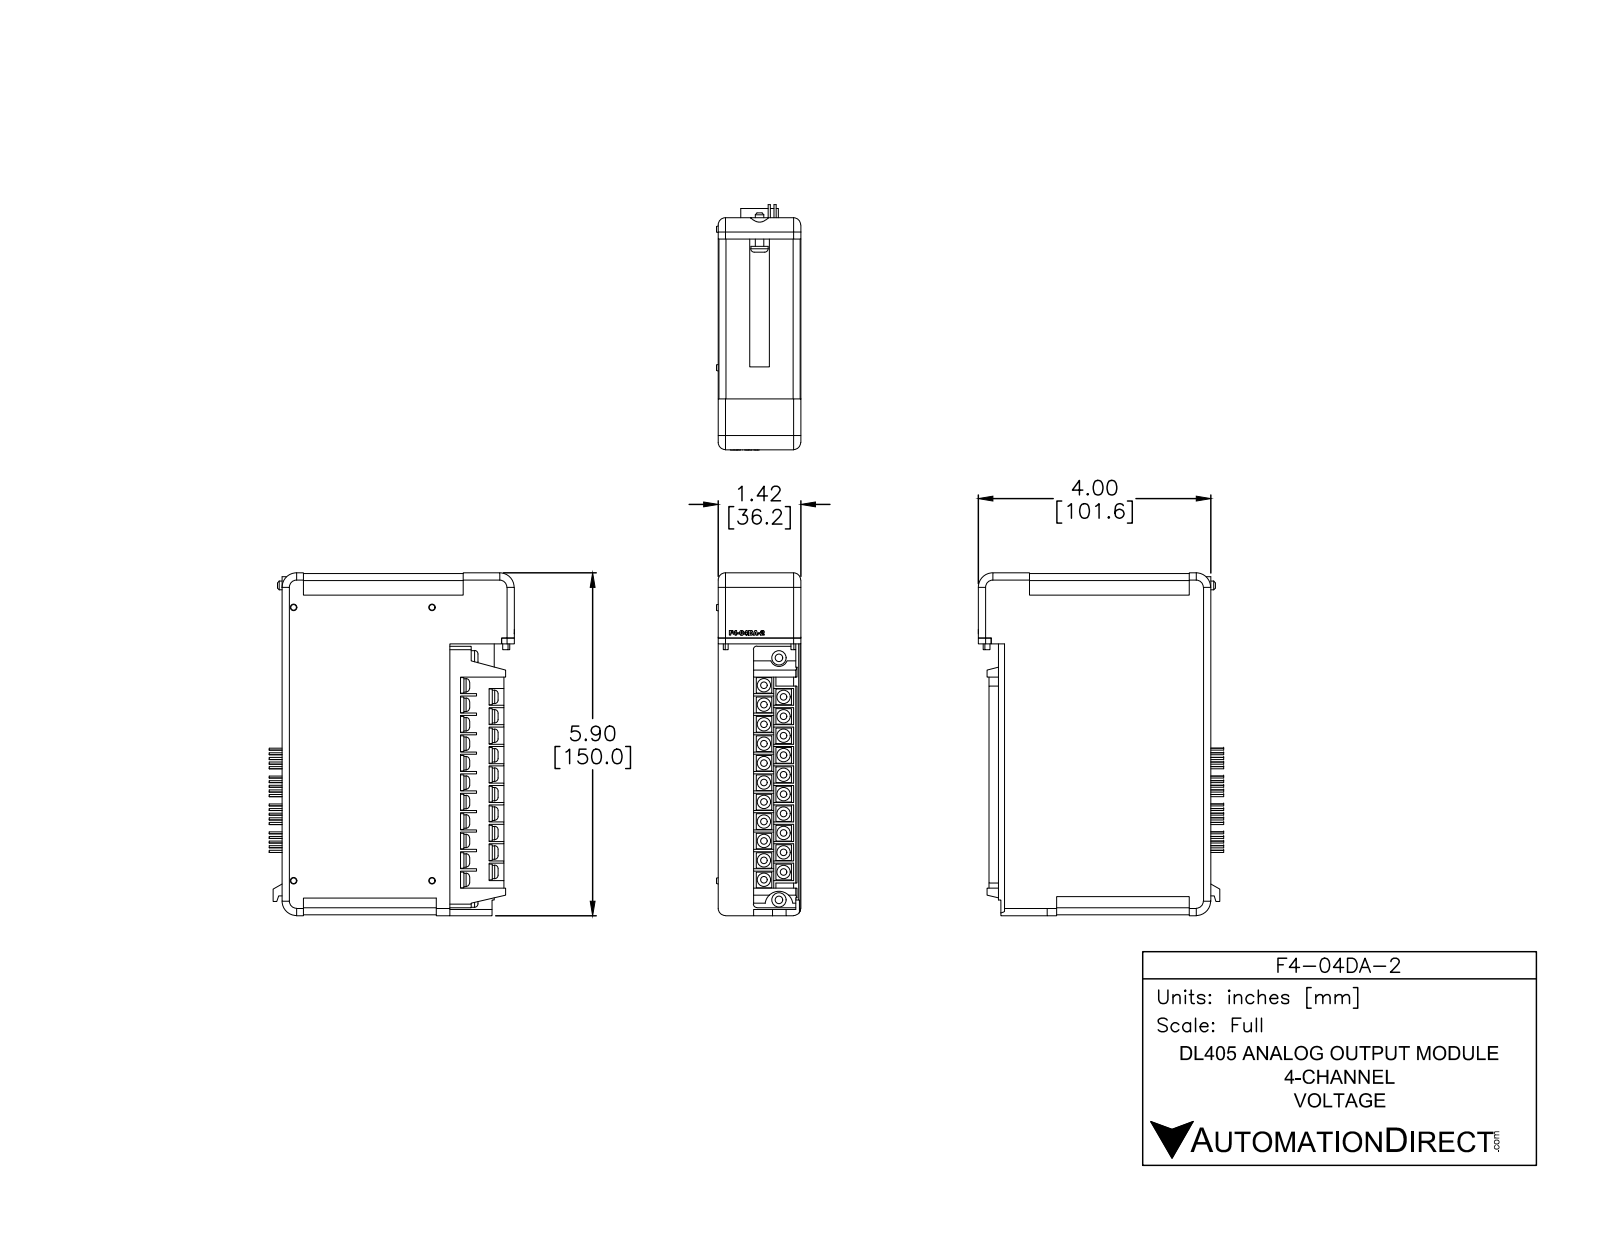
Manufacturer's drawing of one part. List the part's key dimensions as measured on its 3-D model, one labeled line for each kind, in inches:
Part name (STEP PRODUCT): F4-04DA-2
STEP written by: SolidWorks 2014 (AUTOMOTIVE_DESIGN)
Units: inches
Bodies: 15 solids, 608 faces (432 planar, 86 cylindrical, 90 other)
Overall size (bounding box): 5.905 × 4.156 × 1.455
Volume: 27.51 in³ · Surface area: 86.82 in²
Round bosses / shafts (diameter × count): ⌀0.23 ×21, ⌀0.25 ×2, ⌀0.3 ×1, ⌀0.15 ×1
Partial cylindrical surfaces — rounded edges, fillets, slot ends (radius × count): R0.125 ×8, R0.12 ×4, R0.25 ×3, R0.015 ×2, R0.03 ×2, R0.06 ×2, R0.149 ×1, R0.151 ×1
Main face-to-face distances: 1.425, 0.015, 2.89, 5.875, 1.41, 0.47, 0.2, 0.955, 5.89, 1.21
